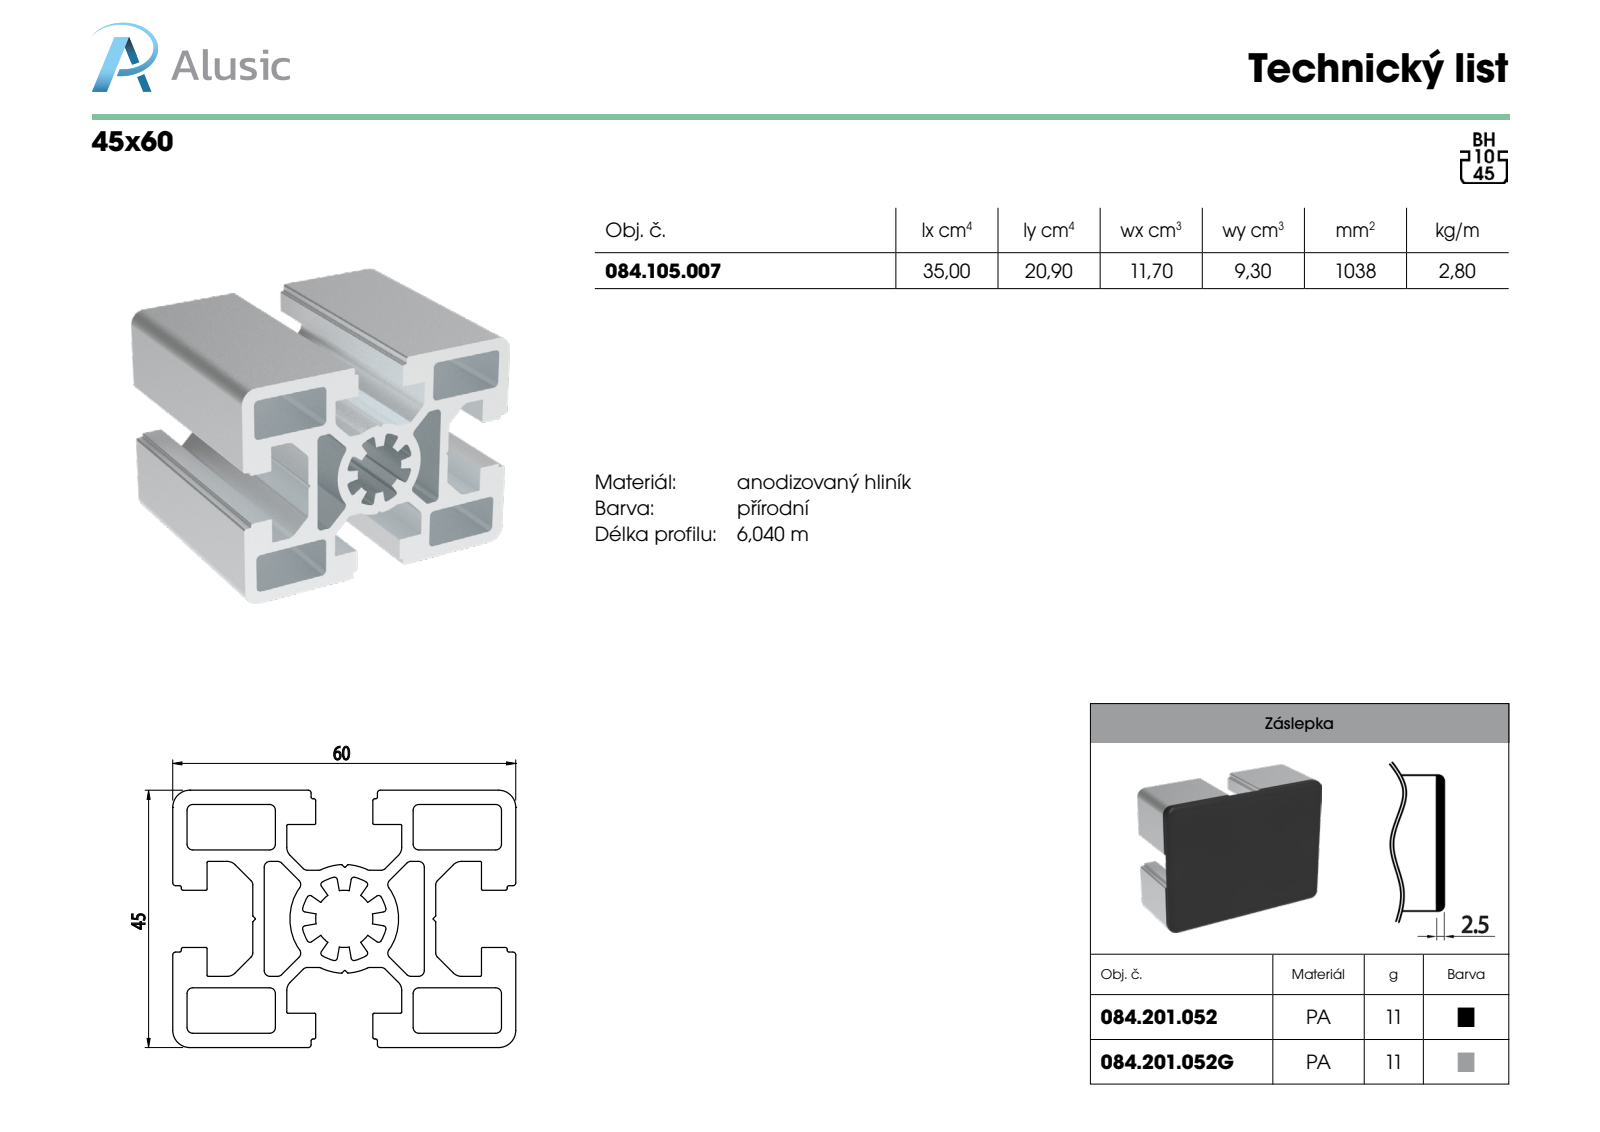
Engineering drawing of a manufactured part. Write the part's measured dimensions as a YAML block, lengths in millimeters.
part_name: "084.105.007"
step_written_by: "SolidWorks 2018 (AUTOMOTIVE_DESIGN)"
units: millimeters
bodies: {solids: 1, faces: 267, planar: 116, cylindrical: 151, other: 0}
overall_size: [100, 60, 45]
volume: 103753
surface_area: 75189
partial_cylinders:
  - {radius: 1, count: 40}
  - {radius: 0.5, count: 24}
  - {radius: 0.2, count: 16}
  - {radius: 0.3, count: 16}
  - {radius: 0.1, count: 12}
  - {radius: 2, count: 8}
  - {radius: 3, count: 4}
  - {radius: 5, count: 1}
face_to_face_distances: [2.5, 2, 7.95, 42.5, 10.45, 34.55, 32.05, 11.5, 40, 3.5]
